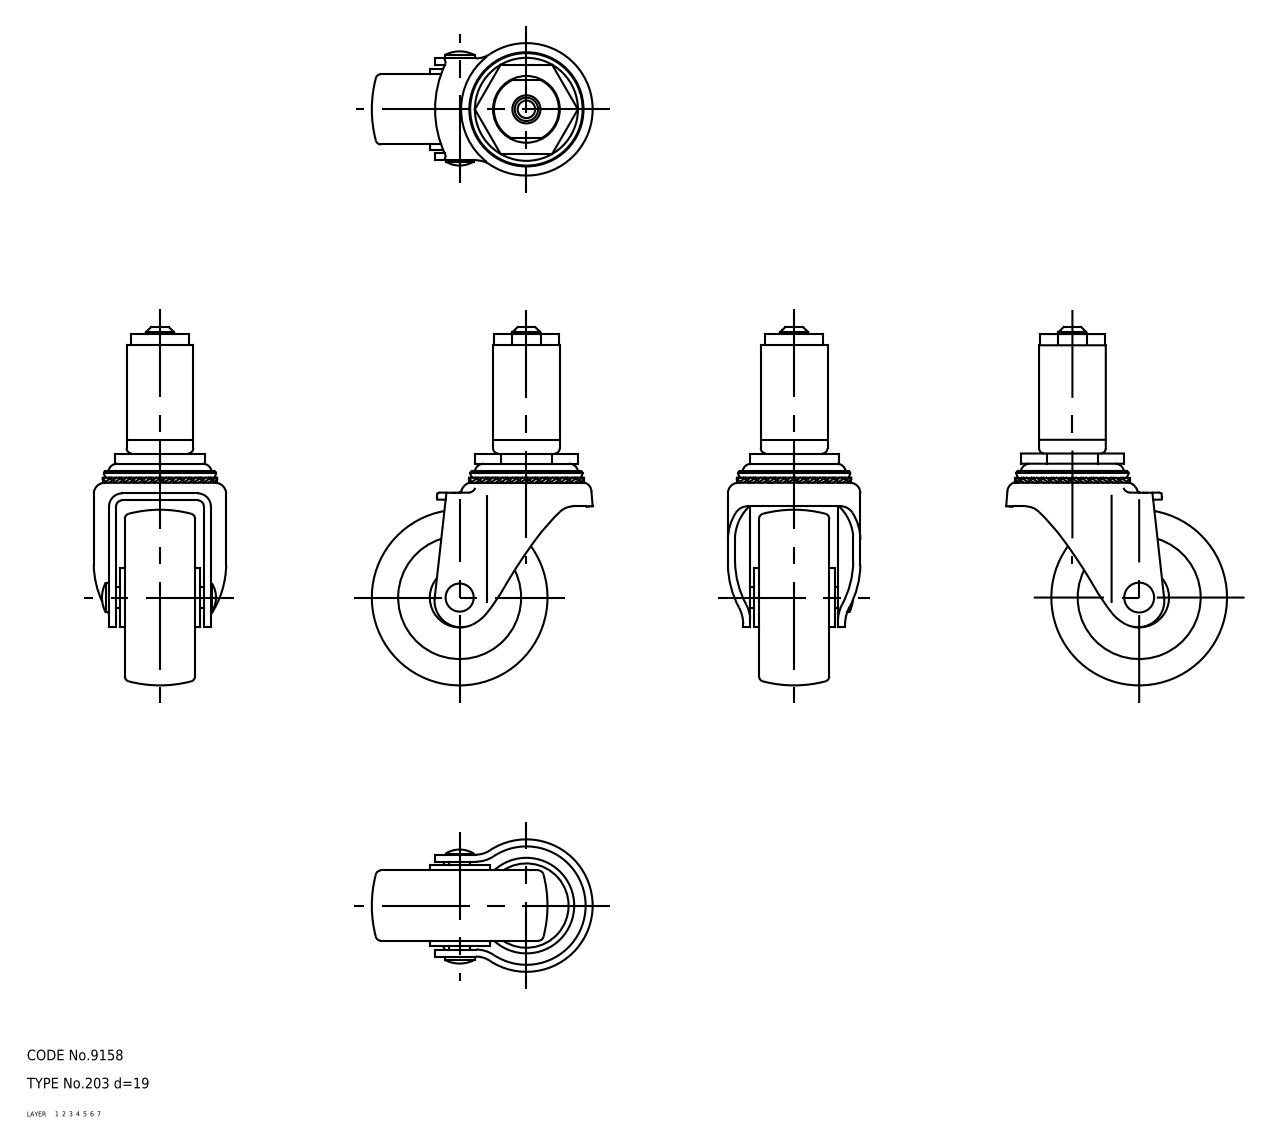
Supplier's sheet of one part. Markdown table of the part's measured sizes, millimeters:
| quantity | value |
| --- | --- |
| part name | wheel; main shaft; axle; No_203_d19_21317_36 |
| STEP written by | CADfix (AUTOMOTIVE_DESIGN) |
| units | millimeters |
| bodies | 4 solids, 186 faces (0 planar, 0 cylindrical, 186 other) |
| overall size | 102 × 62.85 × 37.7 |
| volume | 59 827 mm³ |
| surface area | 20 176 mm² |
